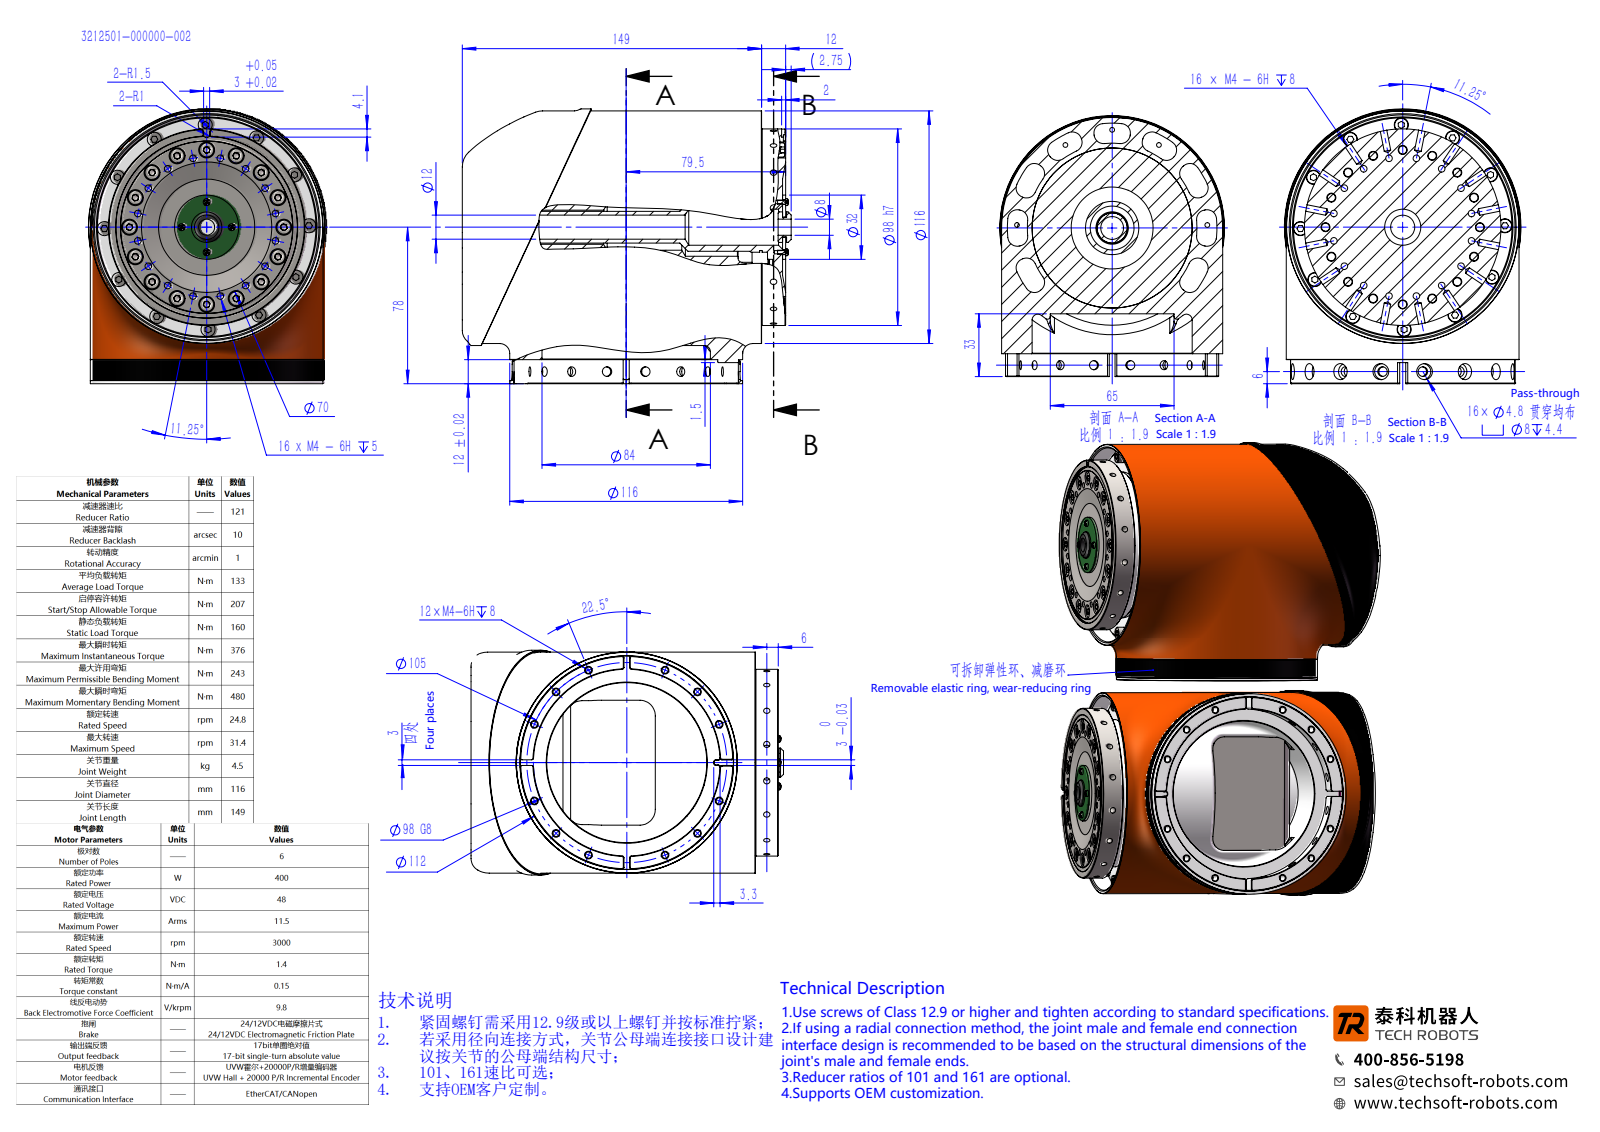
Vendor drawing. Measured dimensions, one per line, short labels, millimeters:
written by: SolidWorks 2016 (CONFIG_CONTROL_DESIGN)
unit: mm
bodies: 22 solids, 1816 faces (647 planar, 703 cylindrical, 466 other)
size: 163.99 × 137 × 118
volume: 1 703 000 mm³; area: 151 103 mm²
holes: 60× ⌀3.3, 44× ⌀4.5, 33× ⌀8, 16× ⌀4.8, 14× ⌀2.5, 4× ⌀1.6, 4× ⌀2.4, 4× ⌀3.5, 4× ⌀6.5, 3× ⌀3.4, 3× ⌀7, 1× ⌀10
bosses: 28× ⌀7, 28× ⌀4, 4× ⌀3.5, 4× ⌀2, 3× ⌀5.5, 3× ⌀3, 1× ⌀118, 1× ⌀116.1
rounds: 24× R1, 4× R1.5, 4× R1.7, 4× R3, 2× R8, 1× R35.3, 1× R57.5
face distances: 12, 139.24, 22, 161.24, 10, 10.5, 1.5, 20.5, 159.74, 149.24
hole spacings: 64.84, 8, 21.6, 34.78, 35, 56.86, 70.34, 46.7
